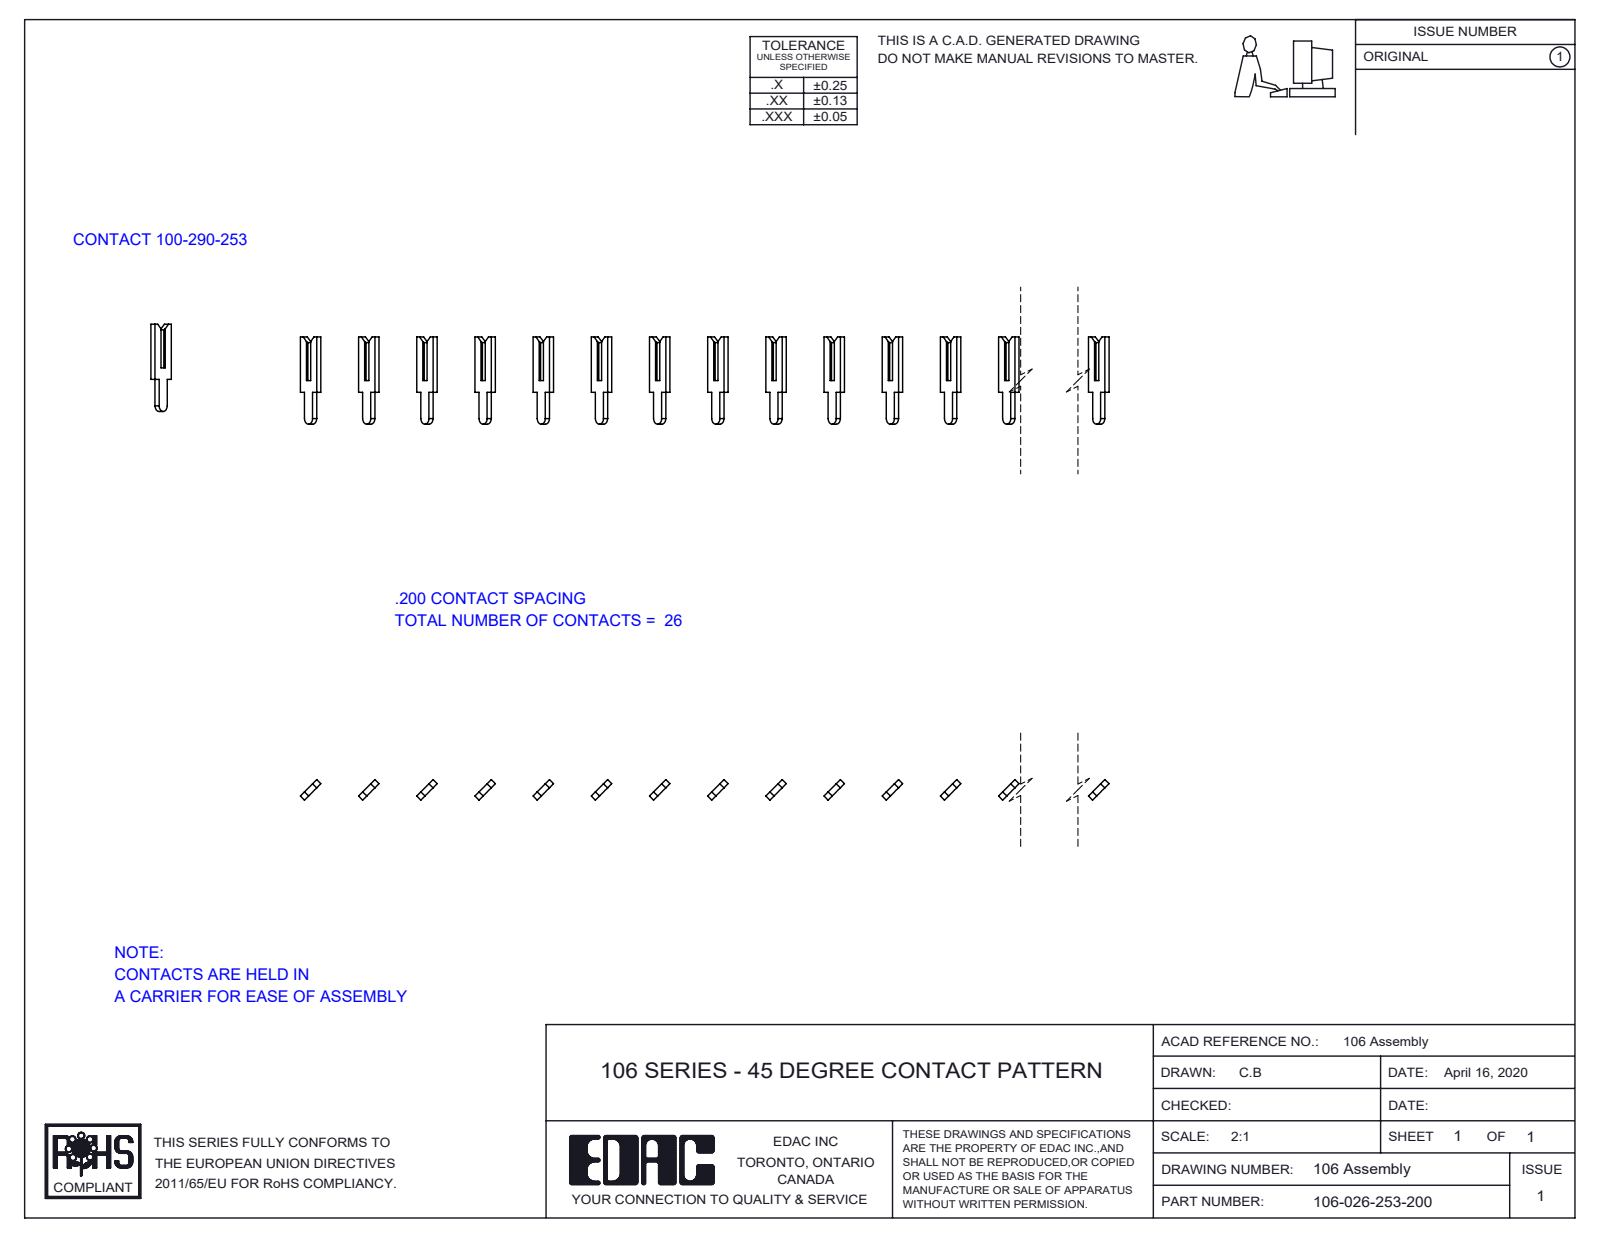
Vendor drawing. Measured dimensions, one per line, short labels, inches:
name: 106-026-253-200; 100-290-001_100-290-253
written by: SolidWorks 2016 (CONFIG_CONTROL_DESIGN)
unit: in
bodies: 26 solids, 520 faces (494 planar, 26 cylindrical, 0 other)
size: 5.071 × 0.3 × 0.071
volume: 0.009 in³; area: 1.387 in²
rounds: 26× R0.019
face distances: 0.141, 0.848, 0.283, 0.99, 0.707, 0.566, 0.424, 1.131, 0.424, 1.838
